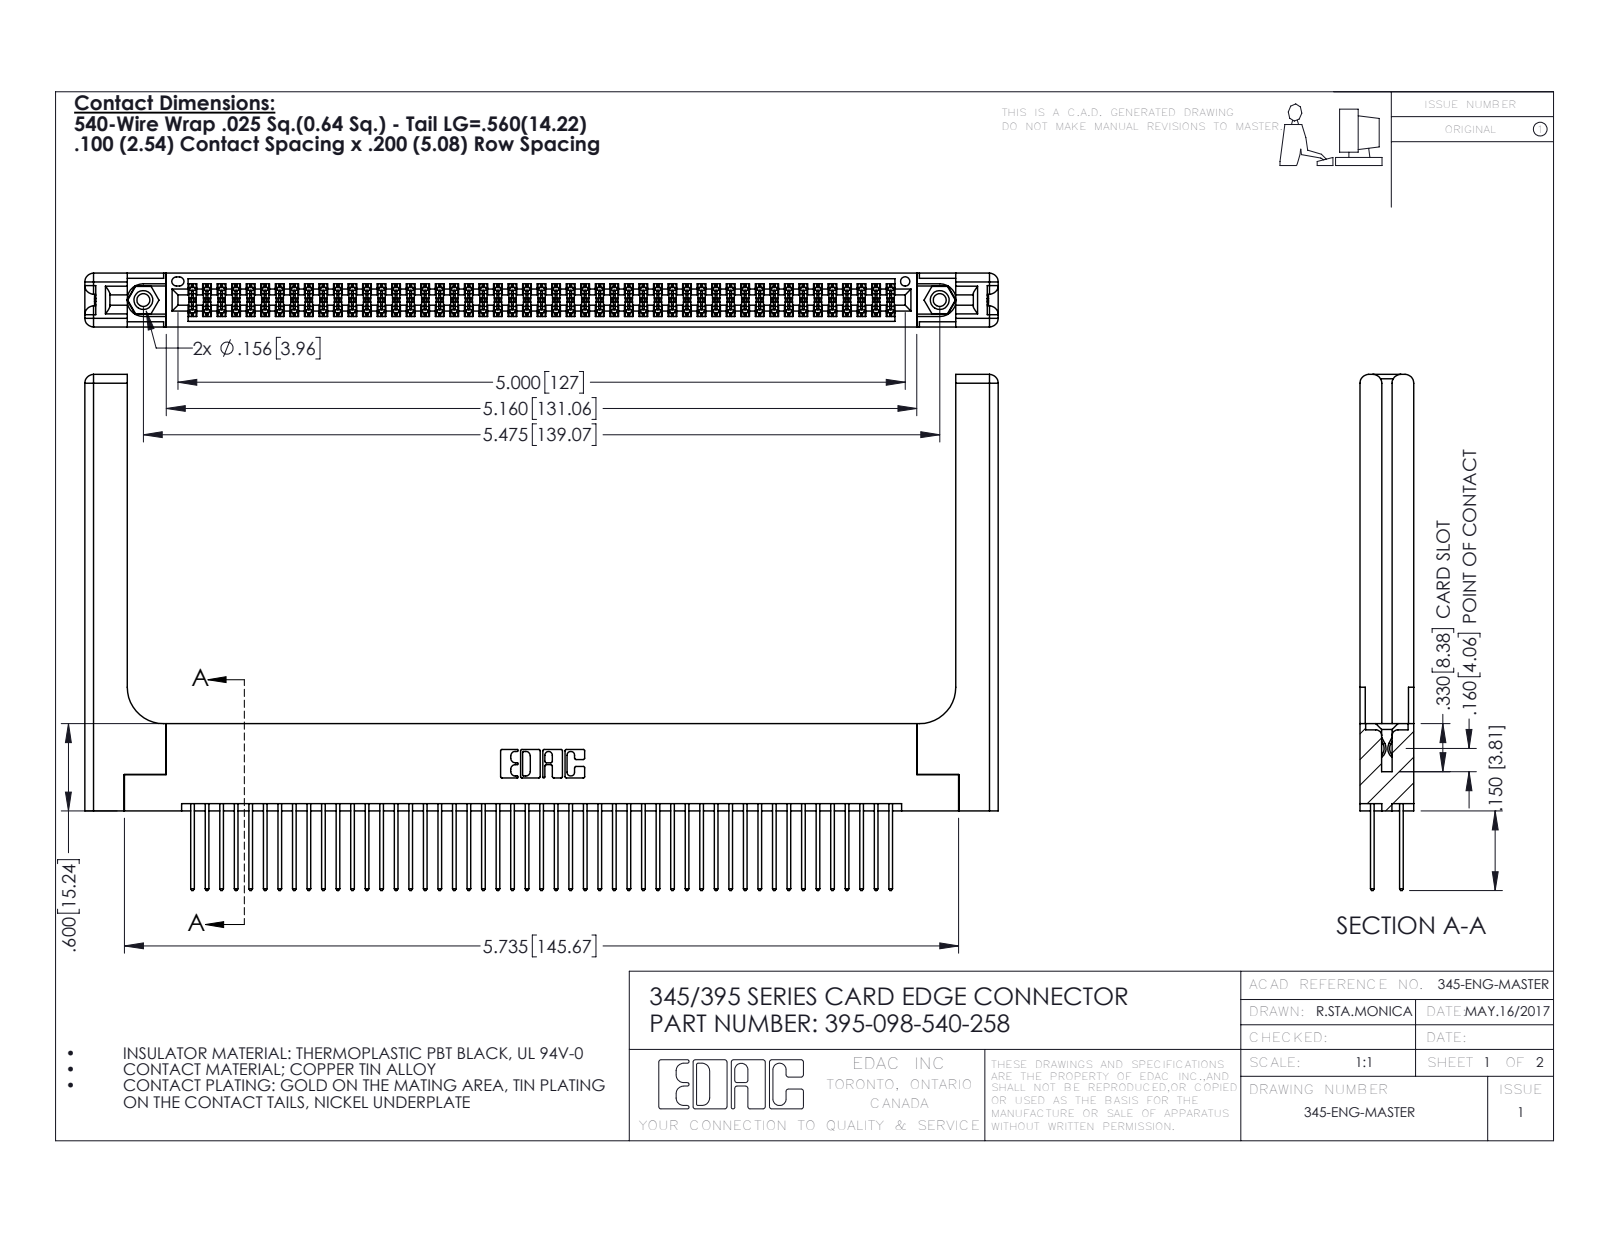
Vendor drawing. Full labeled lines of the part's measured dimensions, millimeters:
Part name (STEP PRODUCT): 345-220-058_345-220-058; 345-250-001_345-250-001-102; 345-292-001_345-293-140; 395-098-540-258 (+1 more)
STEP written by: SolidWorks 2016 (CONFIG_CONTROL_DESIGN)
Units: millimetres
Bodies: 103 solids, 5282 faces (3462 planar, 1760 cylindrical, 60 other)
Overall size (bounding box): 159.5 × 90.1 × 9.4
Volume: 24 400 mm³ · Surface area: 30 460 mm²
Round holes (diameter × count): ⌀2.3 ×2, ⌀3.2 ×2, ⌀4 ×2, ⌀1.6 ×1
Round bosses / shafts (diameter × count): ⌀3.9 ×2
Partial cylindrical surfaces — rounded edges, fillets, slot ends (radius × count): R0.2 ×147, R0.3 ×98, R0.3 ×22, R1.5 ×16, R0.2 ×6, R0.8 ×6, R0.7 ×3, R0.4 ×2
Main face-to-face distances: 1.8, 7.6, 9.4, 5.1, 2.5, 6.9, 0.6, 5.7, 4.4, 3.8
Hole centre spacings: 6.9, 133.1, 139.1
